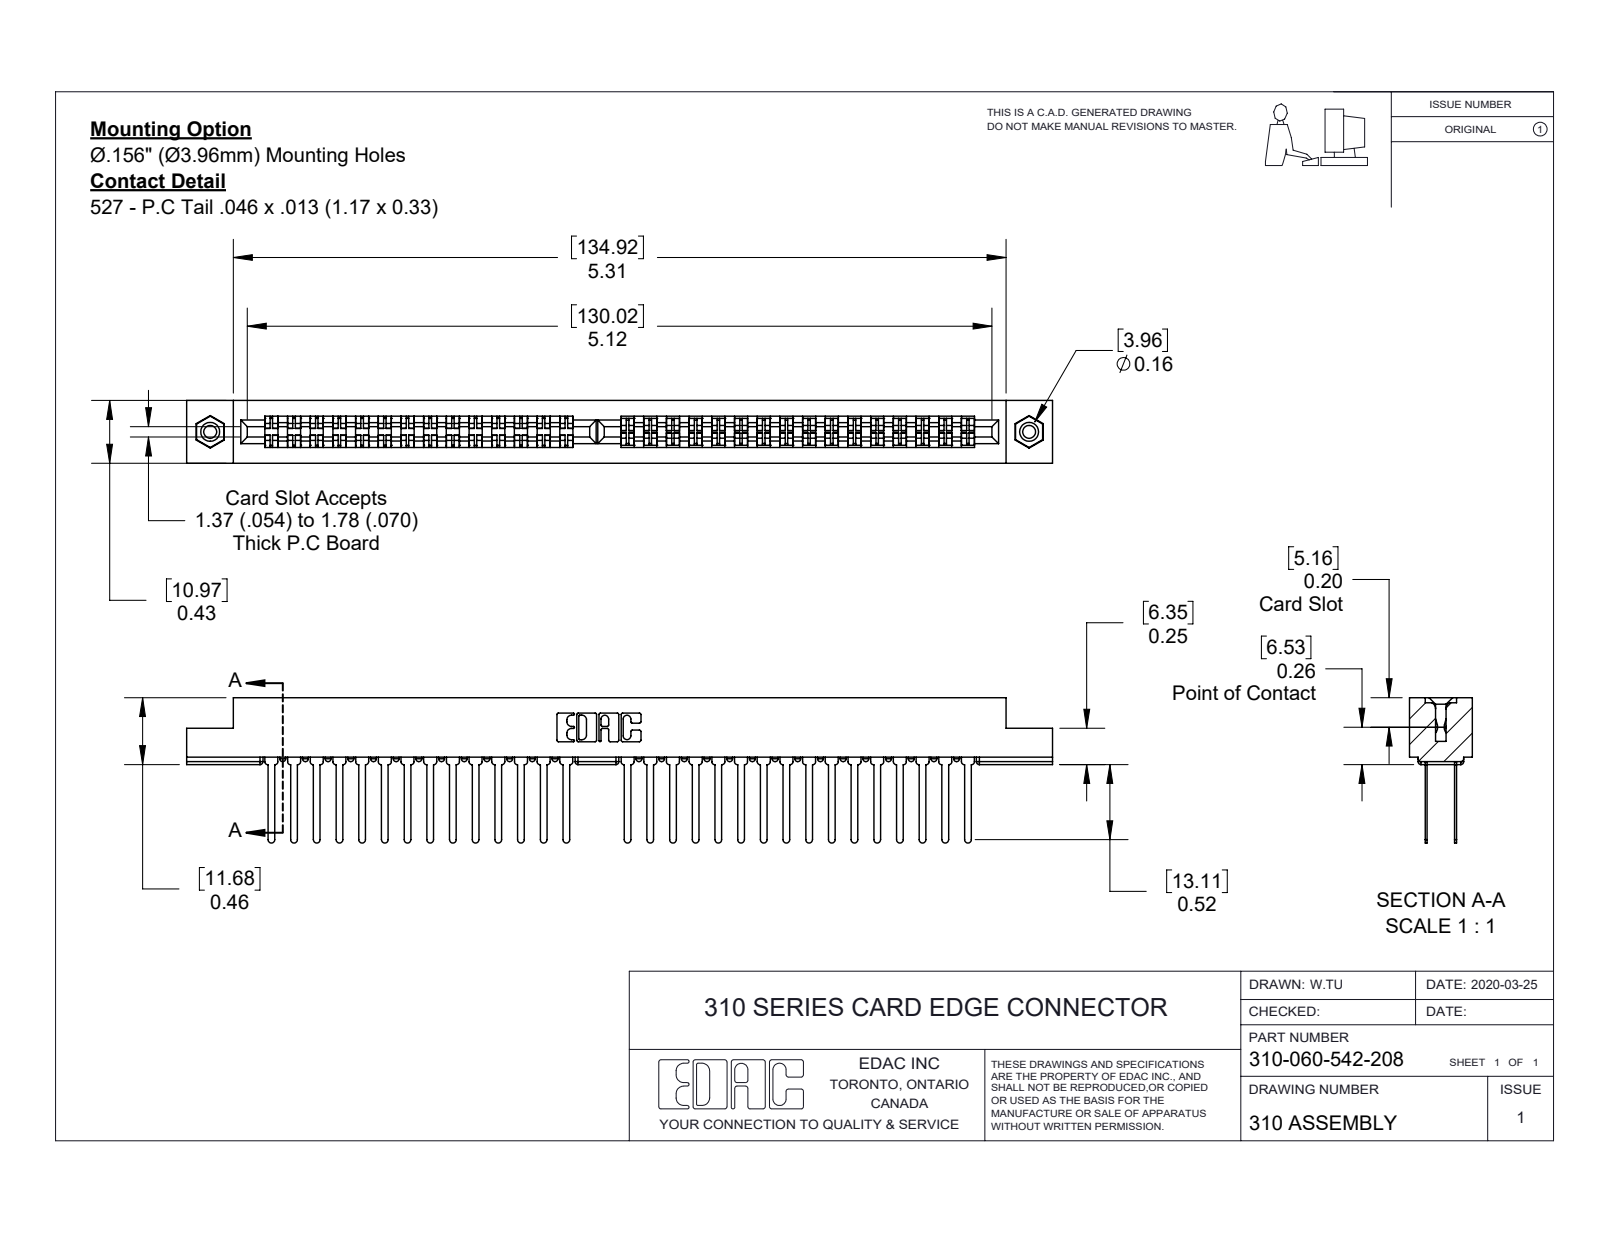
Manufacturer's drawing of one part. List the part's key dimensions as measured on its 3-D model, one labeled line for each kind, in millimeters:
Part name (STEP PRODUCT): 307-290-001_542; 310 Part_.116 Hex; 310-060-542-208; 345-250-001_345-250-003-102
STEP written by: SolidWorks 2016 (CONFIG_CONTROL_DESIGN)
Units: millimetres
Bodies: 63 solids, 2986 faces (1976 planar, 930 cylindrical, 80 other)
Overall size (bounding box): 151.21 × 25.38 × 10.97
Volume: 13 233 mm³ · Surface area: 19 381 mm²
Round holes (diameter × count): ⌀2.26 ×2, ⌀3.17 ×2, ⌀3.96 ×2
Round bosses / shafts (diameter × count): ⌀3.94 ×2
Partial cylindrical surfaces — rounded edges, fillets, slot ends (radius × count): R0.51 ×158, R0.58 ×30, R0.25 ×22, R0.17 ×6, R0.8 ×6, R0.3 ×4, R0.64 ×4, R1.19 ×4
Main face-to-face distances: 2.76, 0.33, 8.22, 0.38, 4.75, 10.98, 5.08, 3.14, 7.84, 5.46
Hole centre spacings: 143
